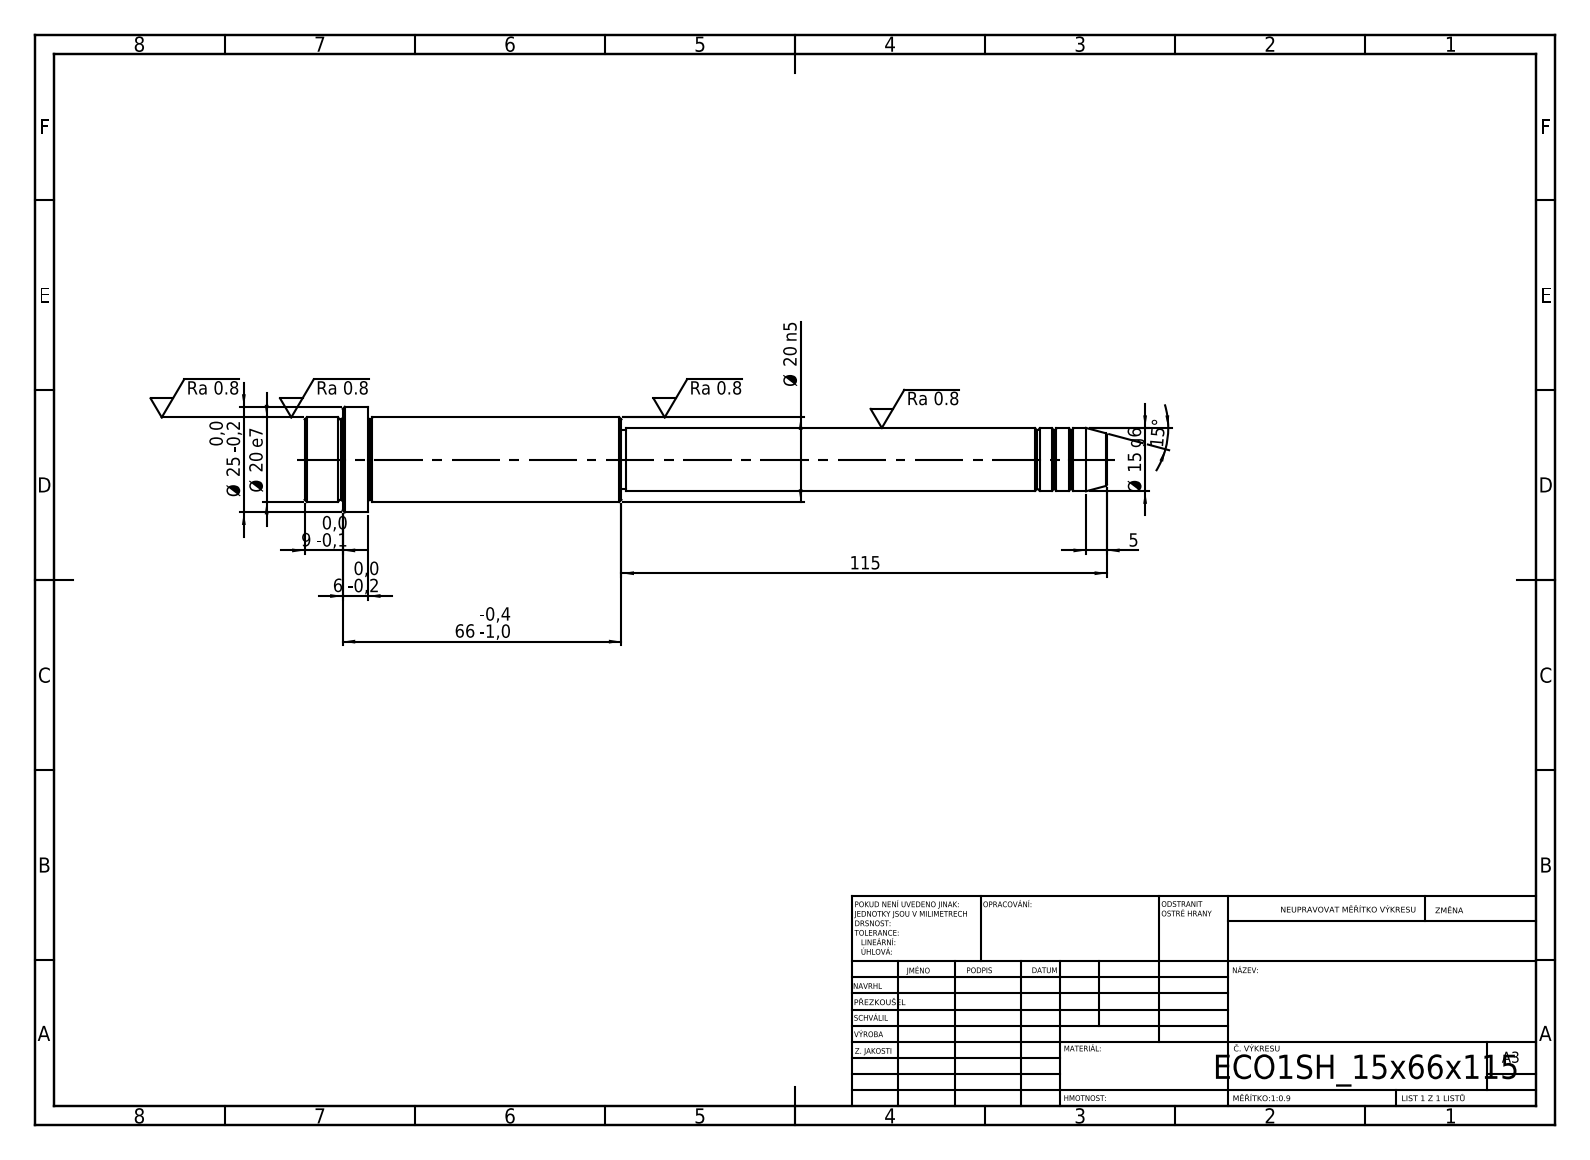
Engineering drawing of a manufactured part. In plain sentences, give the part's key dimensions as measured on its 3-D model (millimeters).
Its 3-D file was written by "SolidWorks 2019 (CONFIG_CONTROL_DESIGN)". It is 1 solid with 52 faces: 6 planar, 16 cylindrical and 30 other. Overall it measures 190 by 25 by 25 millimeters. Its volume is 44 645 cubic millimeters and its surface area 11 251 square millimeters. Round bosses or shafts: 1 of diameter 25, 1 of diameter 20, 1 of diameter 15, 1 of diameter 14. The main face-to-face distances are 15, 6, 9, 60, 66, 75, 115, 175, 181, 190.
